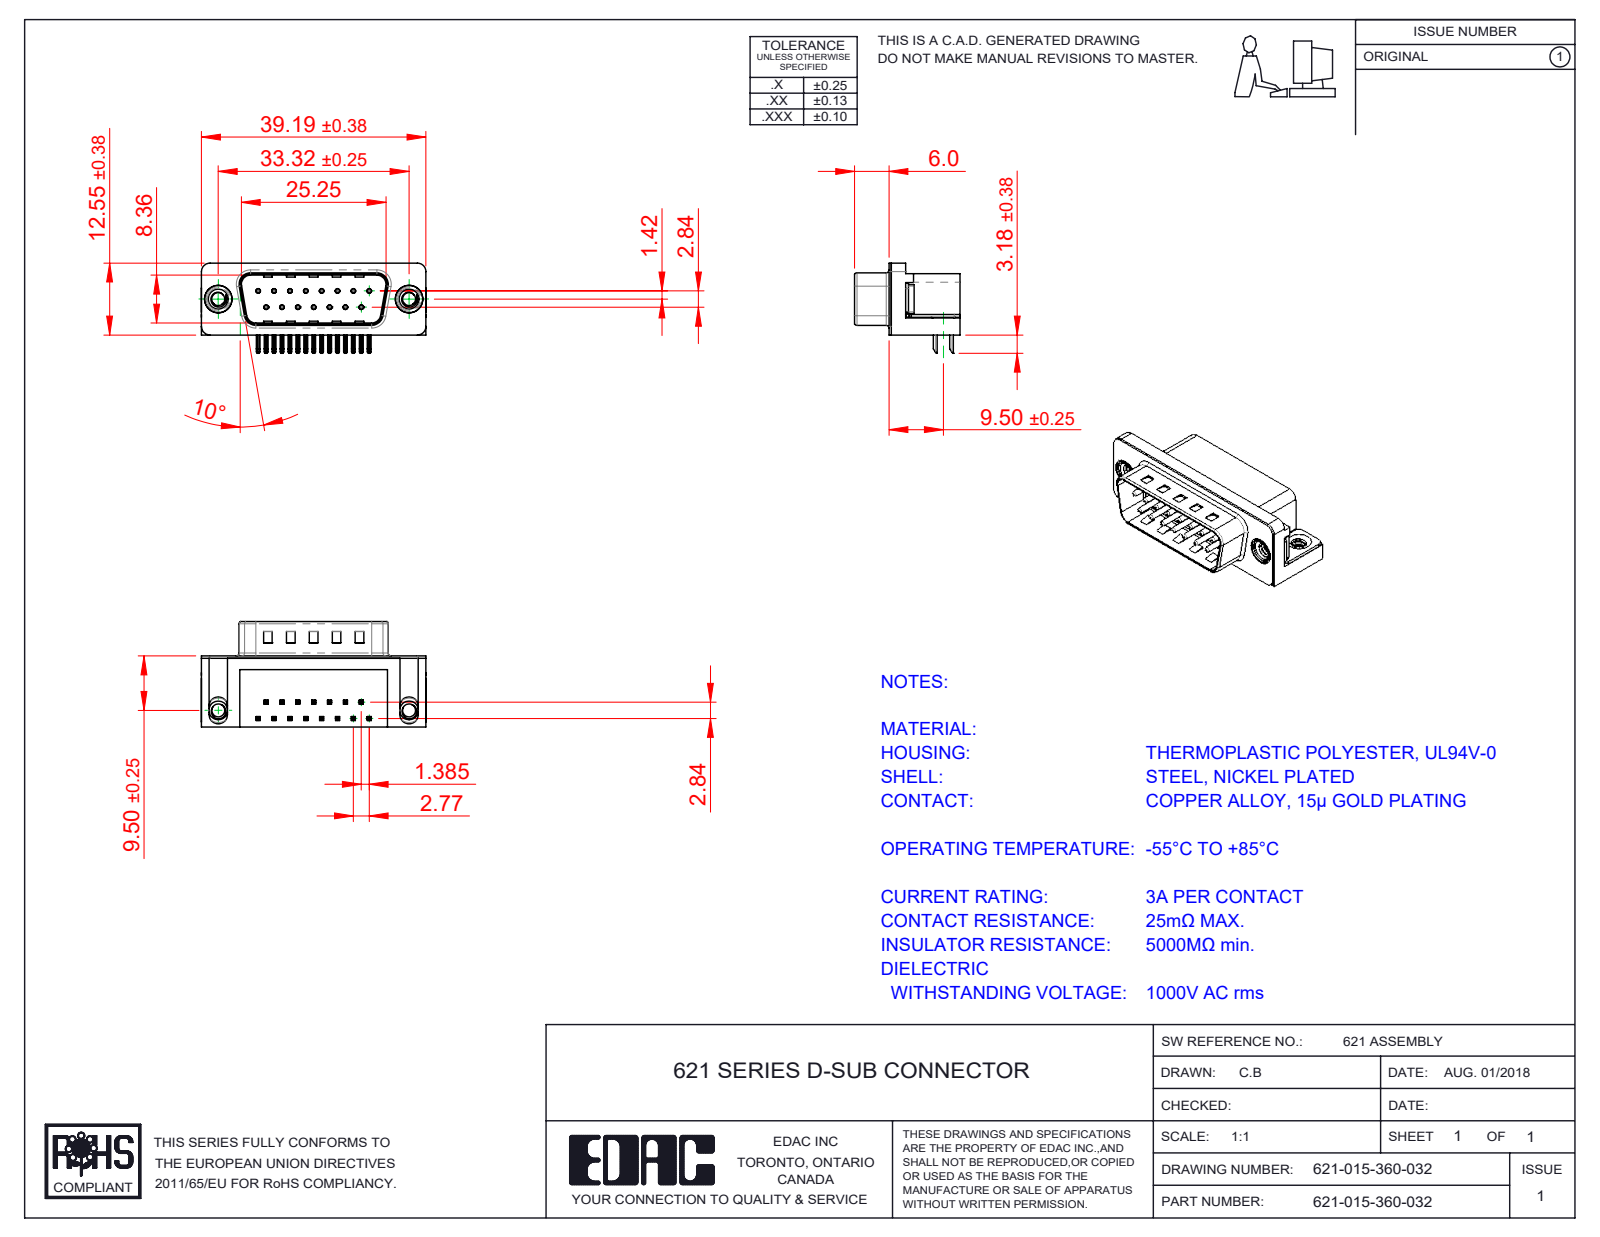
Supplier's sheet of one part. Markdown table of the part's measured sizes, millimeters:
| quantity | value |
| --- | --- |
| part name | 621 Housing_15 Socket; 621 4-40 Threaded Rivet; 621 Contact Top; 621 Contact Bottom (+3 more) |
| STEP written by | SolidWorks 2016 (CONFIG_CONTROL_DESIGN) |
| units | millimeters |
| bodies | 21 solids, 1517 faces (925 planar, 453 cylindrical, 139 other) |
| overall size | 39.22 × 18.4 × 16.25 |
| volume | 4 415 mm³ |
| surface area | 5 656 mm² |
| round holes (diameter × count) | 0.35 × 15, 0.8 × 15, 2.26 × 2, 4 × 2, 4.8 × 2, 5 × 2 |
| round bosses / shafts (diameter × count) | 0.75 × 15, 4.9 × 2, 4.75 × 2, 3.9 × 2 |
| partial cylindrical surfaces (radius × count) | 0.25 × 68, 0.12 × 30, 1 × 16, 0.5 × 14, 1.6 × 8, 1.5 × 6, 0.32 × 4, 0.9 × 4 |
| main face-to-face distances | 0.4, 12, 10.35, 2.1, 10.46, 12.4, 1.7, 10.86, 8.76, 9.5 |
| hole center spacings | 3.16, 2.77, 5.54, 8.31, 11.08, 5.03, 5.04, 7.48 |
